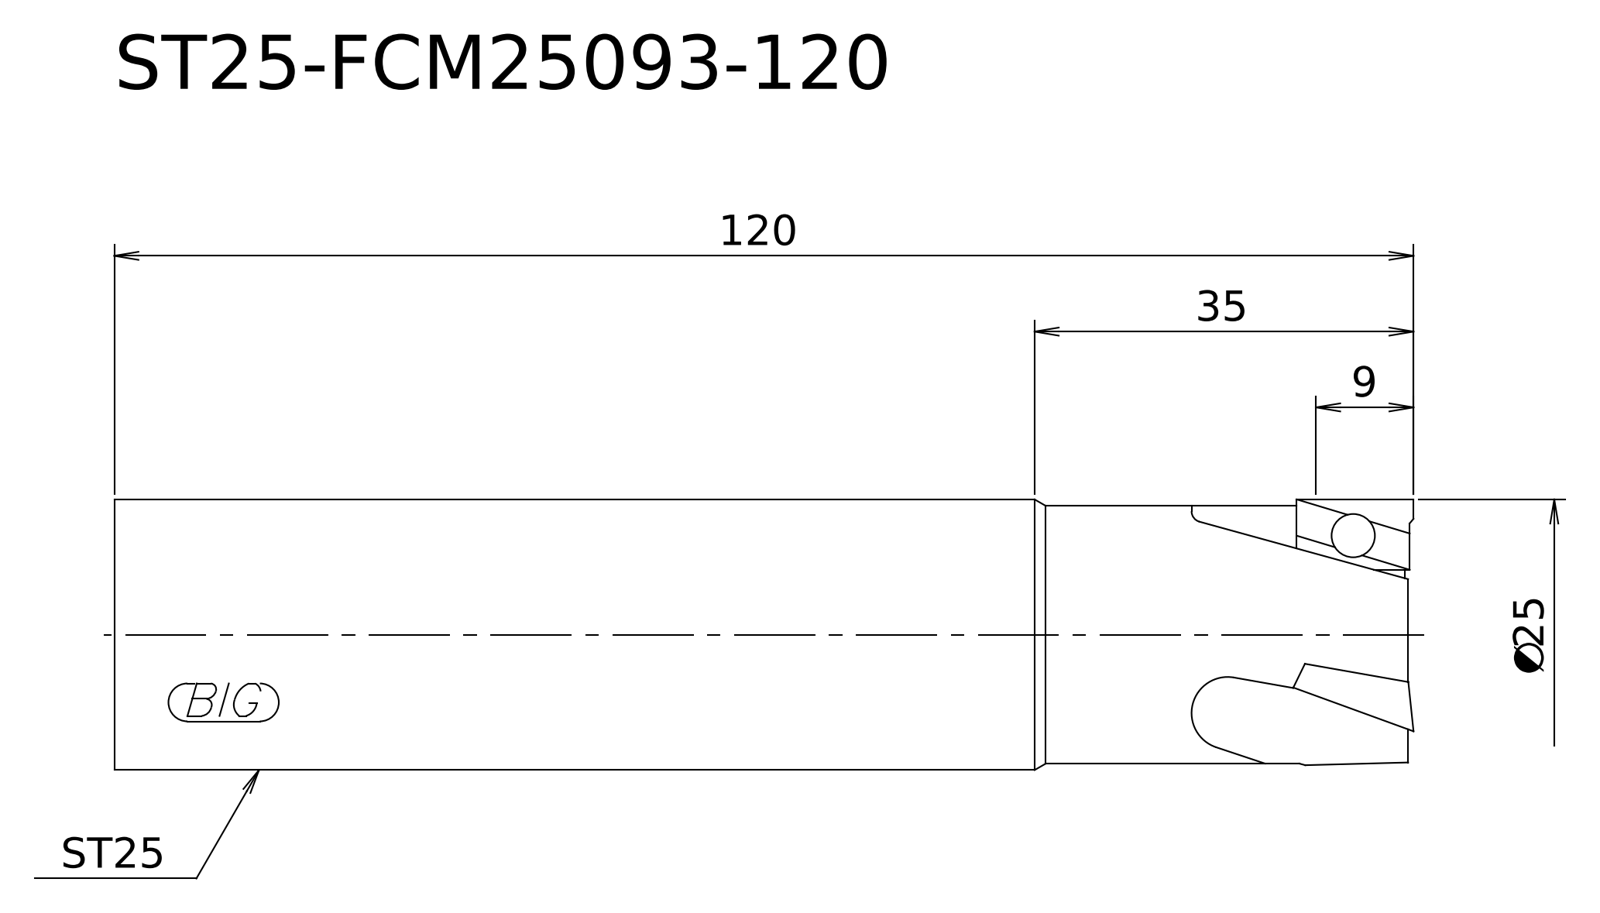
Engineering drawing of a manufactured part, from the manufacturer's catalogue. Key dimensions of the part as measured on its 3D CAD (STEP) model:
STEP written by: Kubotek KeyCreator V8.5.1 (14335) (CONFIG_CONTROL_DESIGN)
Units: millimetres
Bodies: 1 solid, 7 faces (3 planar, 3 cylindrical, 1 other)
Overall size (bounding box): 120 × 25 × 25
Volume: 57 815 mm³ · Surface area: 10 376 mm²
Round bosses / shafts (diameter × count): ⌀25 ×1, ⌀23.8 ×1
Main face-to-face distances: 120, 10.79, 109.21
